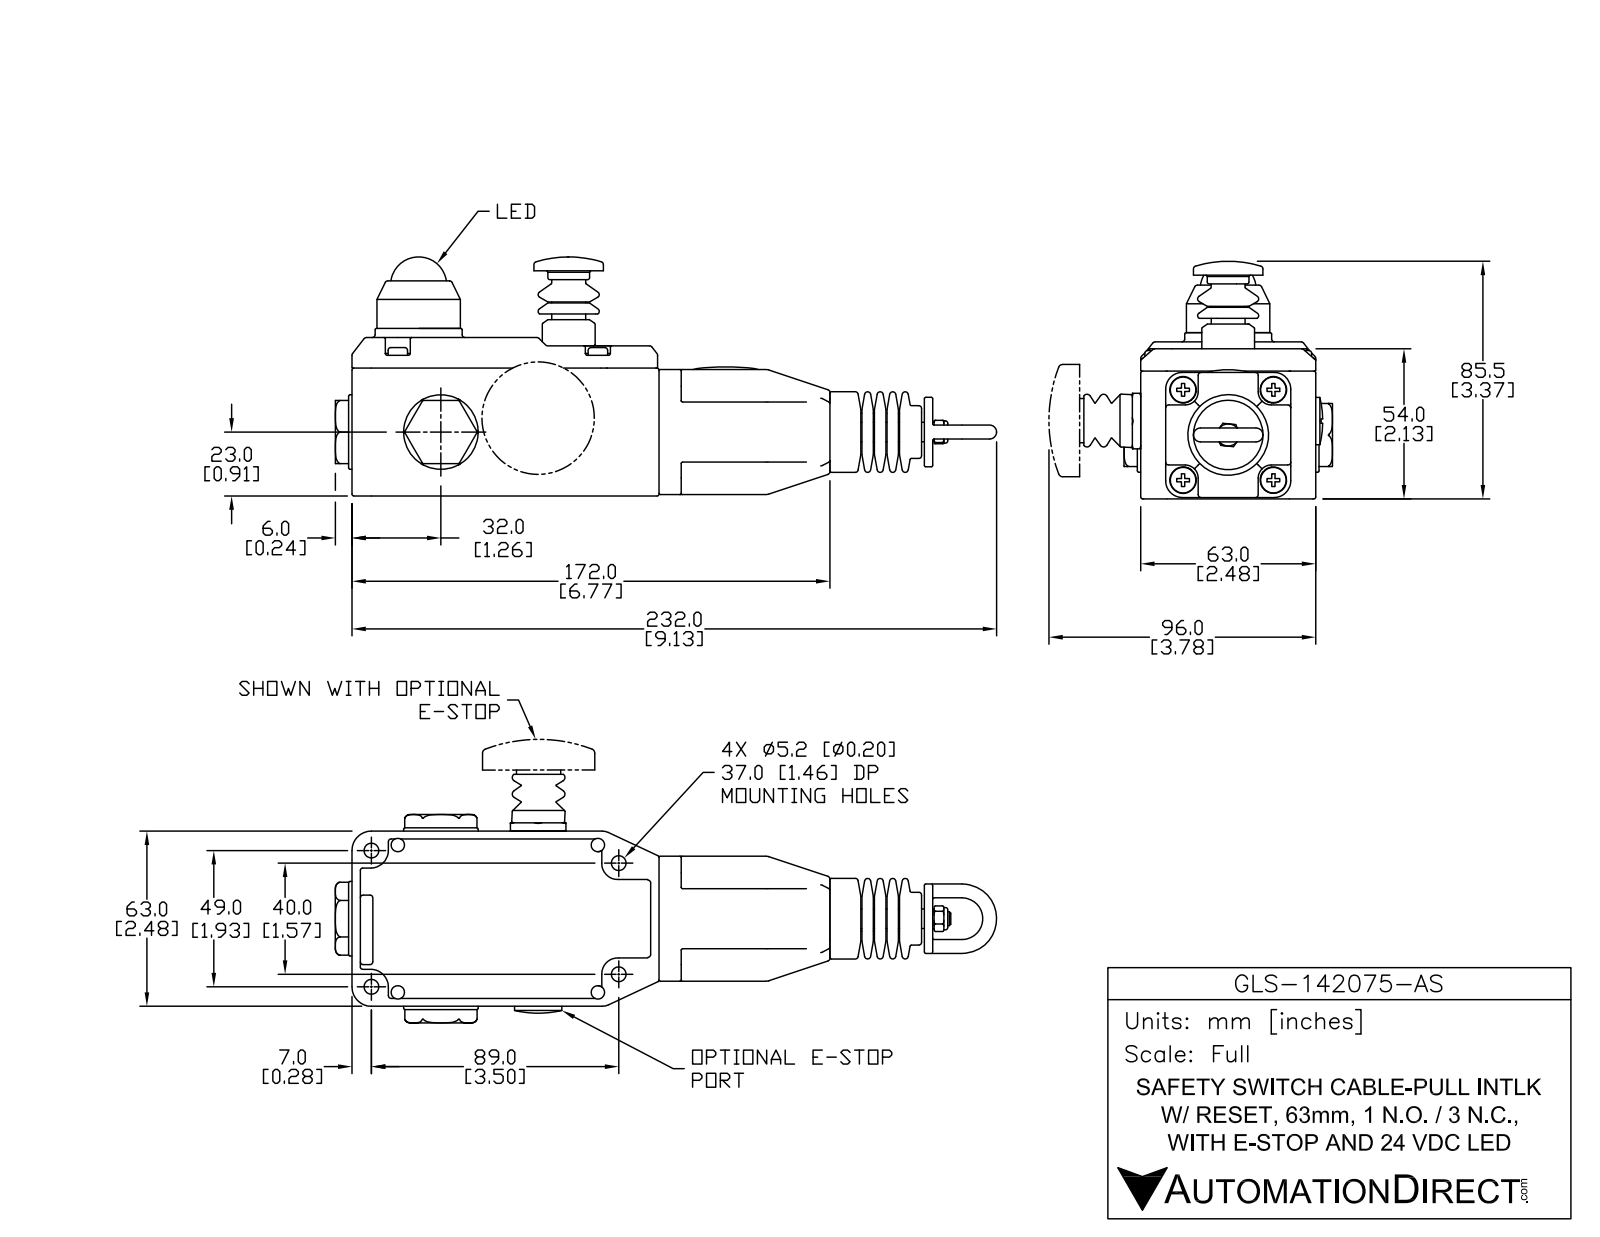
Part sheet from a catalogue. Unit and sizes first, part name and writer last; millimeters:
Units: millimetres
Overall size (bounding box): 238 × 102.3 × 86
Round holes (diameter × count): ⌀4.75 ×4, ⌀9.5 ×4, ⌀5 ×2, ⌀5.2 ×2, ⌀15 ×1, ⌀34 ×1
Round bosses / shafts (diameter × count): ⌀9.2 ×4, ⌀6 ×4, ⌀26.8 ×2, ⌀25 ×2, ⌀12 ×2, ⌀5 ×2, ⌀40 ×1, ⌀31.3 ×1
Partial cylindrical surfaces — rounded edges, fillets, slot ends (radius × count): R0.5 ×52, R0.75 ×20, R1.1 ×6, R4 ×4, R4.5 ×4, R4.8 ×4, R16 ×4, R5.8 ×2
Main face-to-face distances: 63, 54, 56.68, 9, 3, 11.7, 33.3, 53.68, 45, 4.5
Hole centre spacings: 9.6, 9.62, 26.78, 29.22, 32.4, 32.6, 45.96, 46.61
Volume: 516 211 mm³ · Surface area: 66 955 mm²
Bodies: 2 solids, 684 faces (222 planar, 225 cylindrical, 237 other)
Part name (STEP PRODUCT): GLS-142075-AS
STEP written by: SolidWorks 2013 (AUTOMOTIVE_DESIGN)
